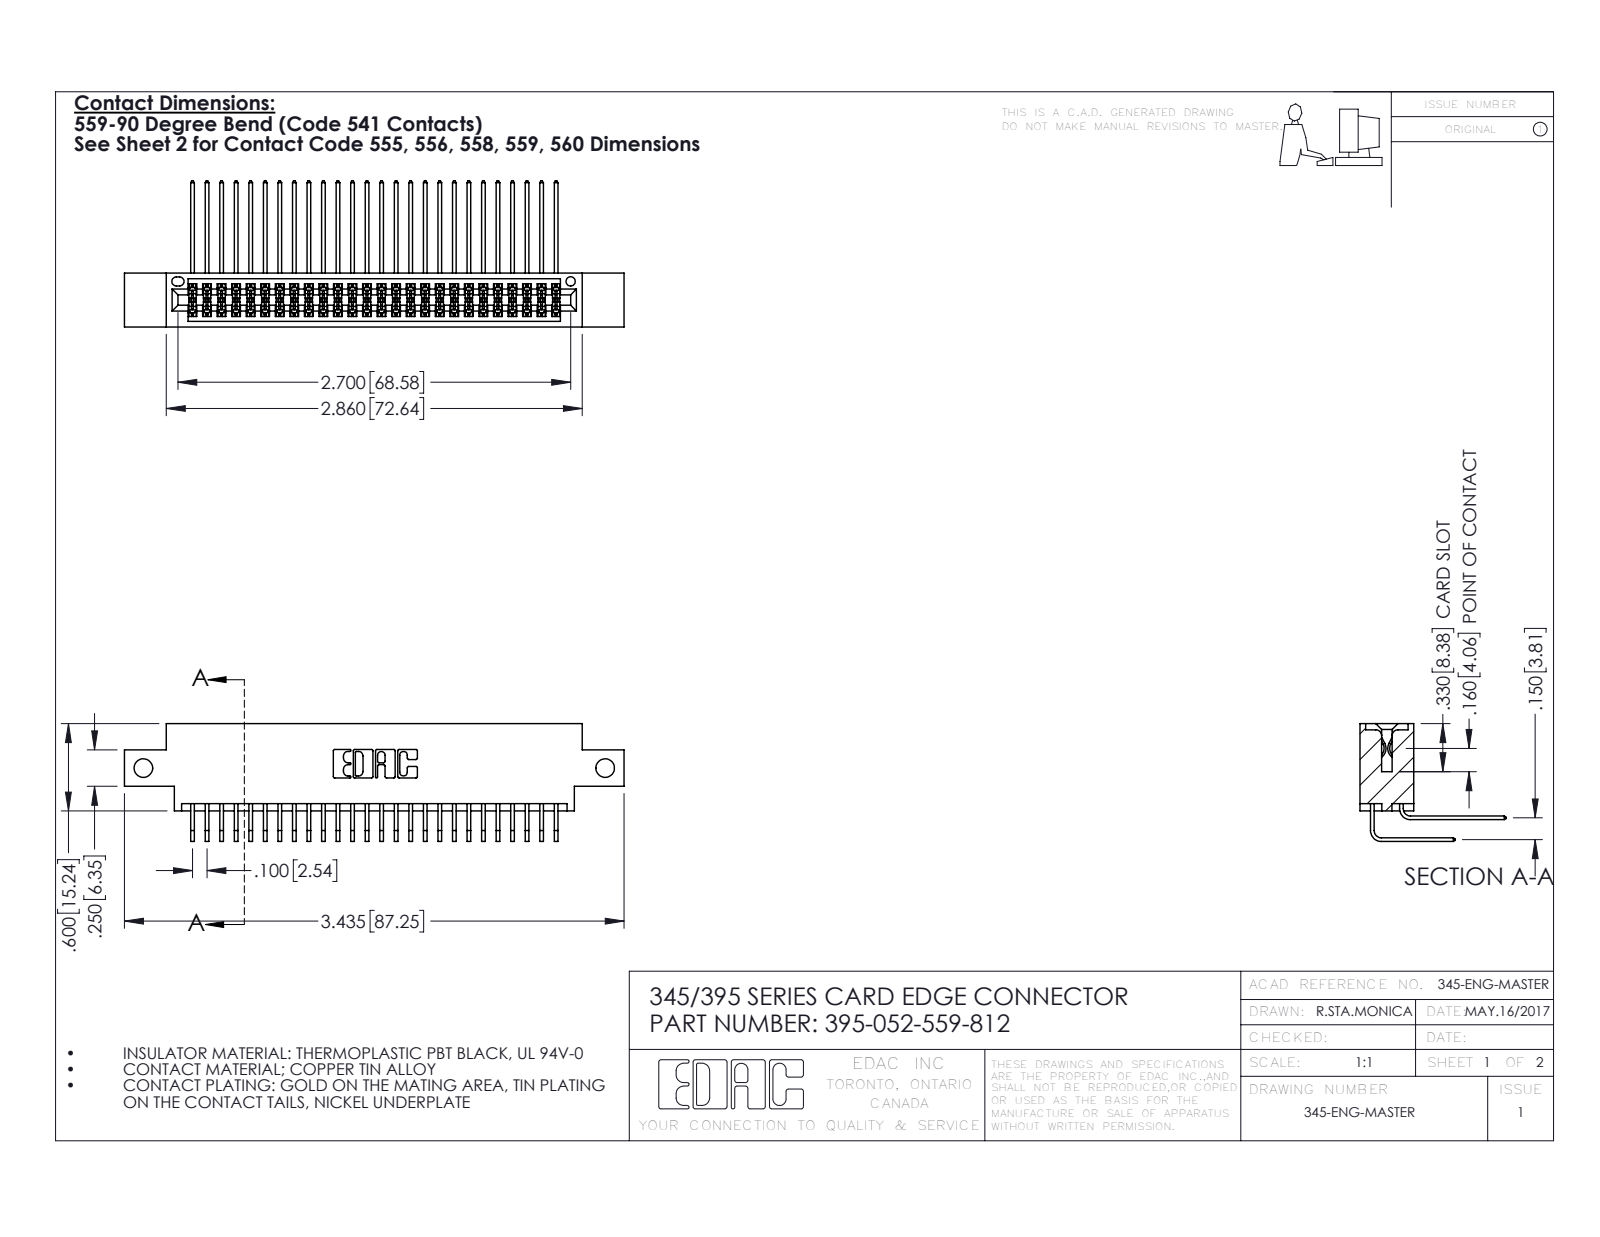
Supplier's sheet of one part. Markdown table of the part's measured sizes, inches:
| quantity | value |
| --- | --- |
| part name | 345 Part_0.170 Offset - Side Mount; 395-052-559-812; 345-292-001_559 Tail - 2; 345-292-001_558 559 Tail - 1 |
| STEP written by | SolidWorks 2016 (CONFIG_CONTROL_DESIGN) |
| units | inches |
| bodies | 53 solids, 2834 faces (1904 planar, 930 cylindrical, 0 other) |
| overall size | 3.435 × 1.005 × 0.809 |
| volume | 0.514 in³ |
| surface area | 21.02 in² |
| round holes (diameter × count) | 0.128 × 2, 0.064 × 1 |
| partial cylindrical surfaces (radius × count) | 0.006 × 79, 0.01 × 22, 0.007 × 6, 0.031 × 6, 0.026 × 3, 0.014 × 2, 0.019 × 2, 0.022 × 2 |
| main face-to-face distances | 0.072, 0.298, 0.37, 0.2, 0.098, 0.272, 0.025, 0.15, 0.225, 0.175 |
| hole center spacings | 3.175 |
